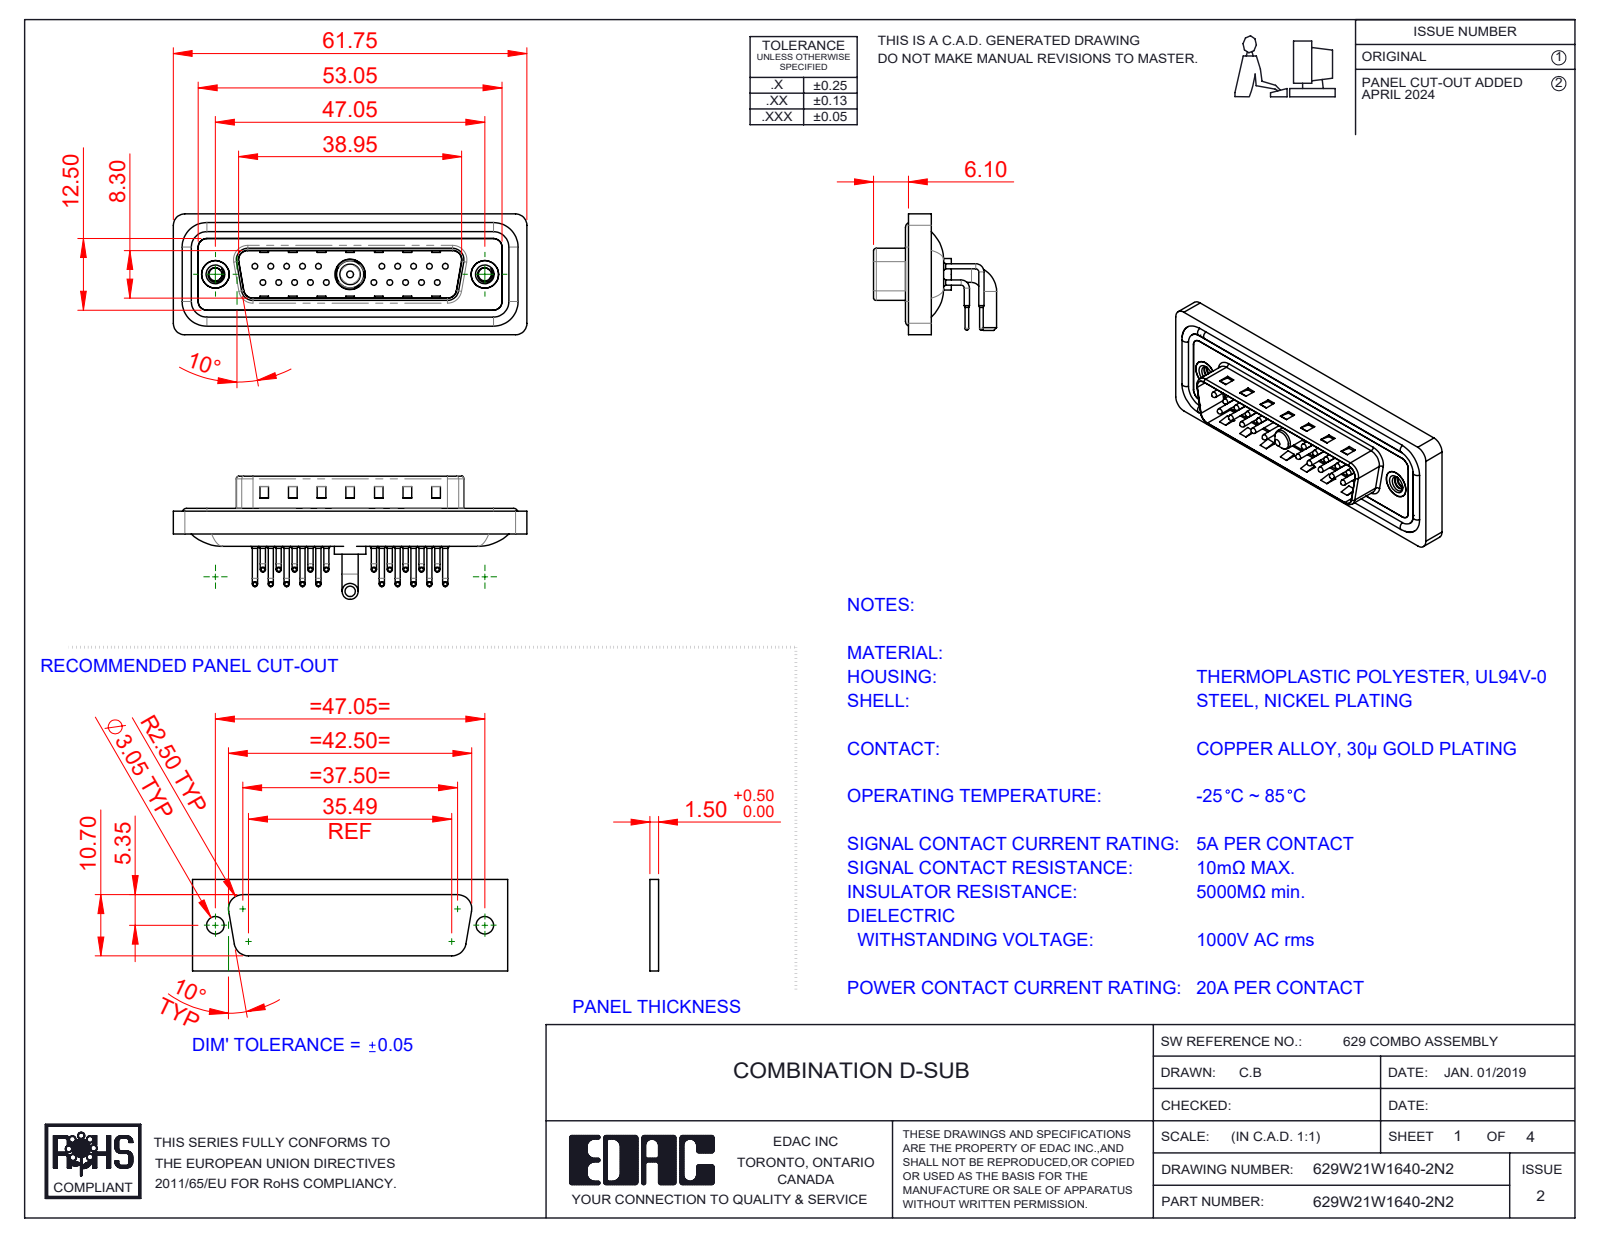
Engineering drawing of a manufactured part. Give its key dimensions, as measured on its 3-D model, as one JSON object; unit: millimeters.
{"part_name": "629Combo Shell Rear_25 Contacts; Power Pin_20A RA; 629W21W1640-2N2; 629Combo Contact Row 1 (+5 more)", "step_written_by": "SolidWorks 2023 (CONFIG_CONTROL_DESIGN)", "units": "millimeters", "bodies": {"solids": 29, "faces": 2726, "planar": 1499, "cylindrical": 929, "other": 298}, "overall_size": [61.75, 21.5, 21.1], "volume_mm3": 7429, "surface_area_mm2": 12721, "round_holes": [[0.75, 20], [1.6, 20], [2, 20], [2.26, 2], [4, 2], [4.8, 2], [5, 2], [4.85, 1], [5.3, 1]], "round_bosses_or_shafts": [[0.9, 40], [1.5, 20], [1, 20], [0.65, 20], [1.6, 4], [4.9, 2], [2.8, 2], [5.5, 1]], "partial_cylinders_radius": [[1.01, 20], [1.5, 18], [2, 18], [0.5, 8], [1.6, 8], [0.25, 4], [0.6, 4], [0.65, 4]], "face_to_face_distances": [0.4, 2.9, 0.8, 4.1, 1.1, 2.1, 1.6, 4.5, 1.5, 2.5], "hole_center_spacings": [3.16, 2.77, 5.54, 8.31, 5.04, 19.39, 20.97, 22.16]}
